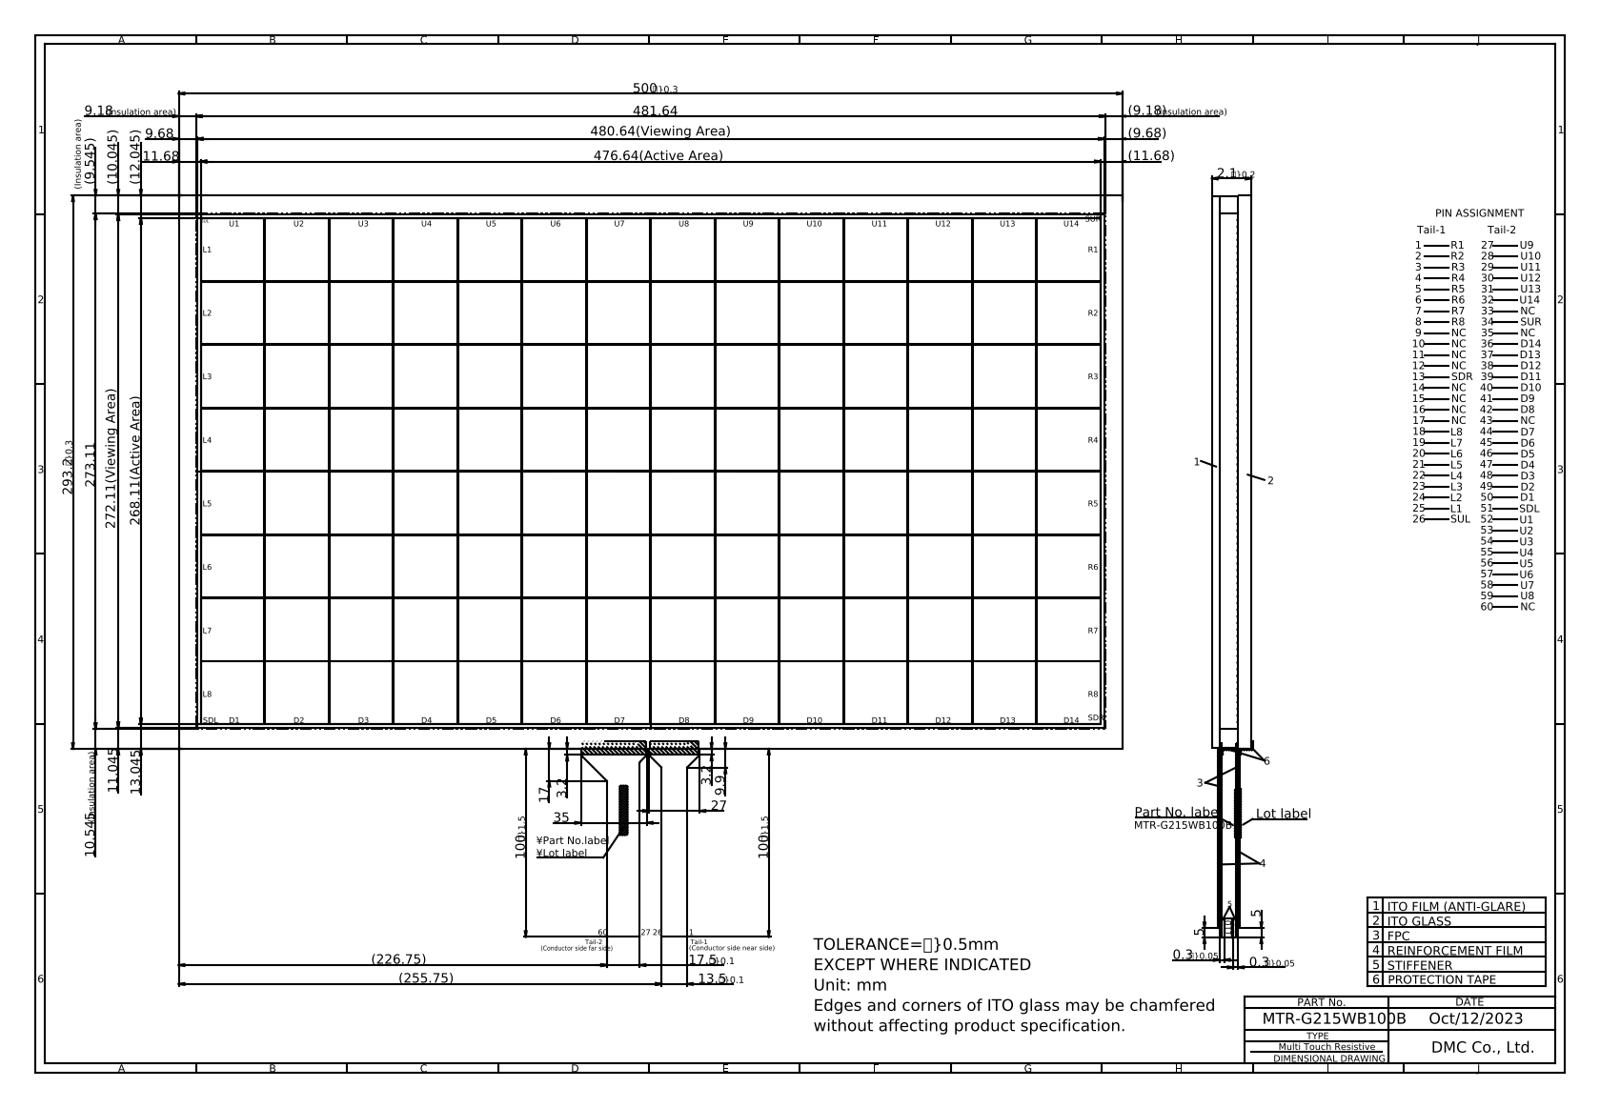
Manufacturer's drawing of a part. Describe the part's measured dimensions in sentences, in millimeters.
The part is named "MTR-G215WB100B". Its 3-D file was written by "Autodesk Inventor 2020 (CONFIG_CONTROL_DESIGN)". It is 1 solid with 294 faces: 282 planar, 12 cylindrical and 0 other. Overall it measures 700 by 451.84 by 2.2 millimeters. Its volume is 307 973 cubic millimeters and its surface area 303 621 square millimeters. Partial cylindrical surfaces (rounded edges, fillets, slot ends): 8 of radius 1, 4 of radius 0.2. The main face-to-face distances are 2.1, 1.8, 1.9, 2, 293.2, 500, 0.4, 2.2, 0.5, 0.7.
